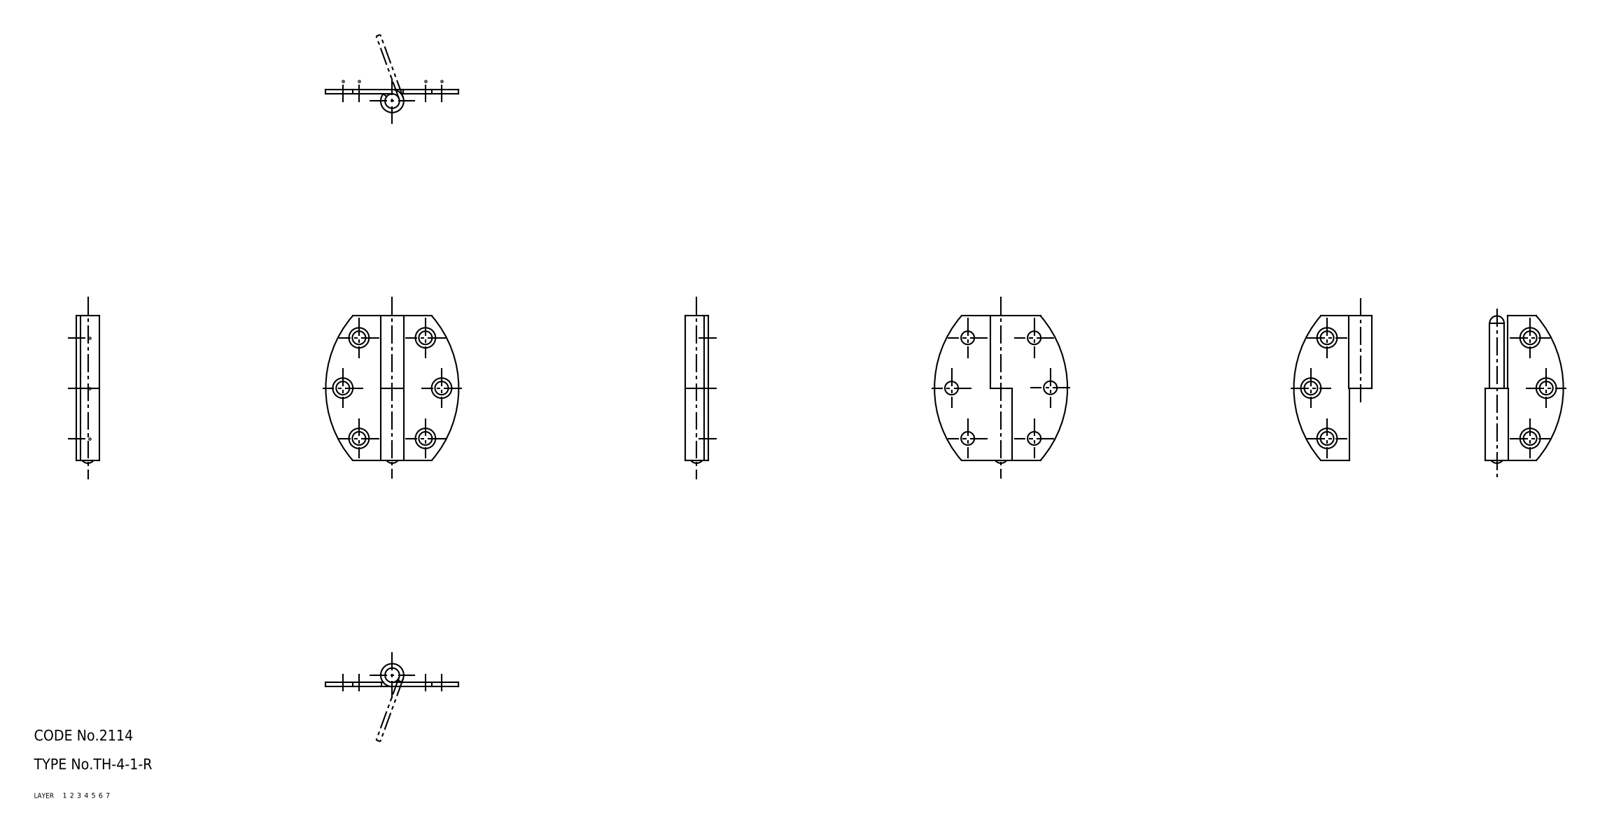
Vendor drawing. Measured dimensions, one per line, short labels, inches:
name: shaft; hinge piece_B; hinge piece_A; TH_4_1_R_8987_36
written by: CADfix (AUTOMOTIVE_DESIGN)
unit: in
bodies: 3 solids, 48 faces (0 planar, 0 cylindrical, 48 other)
size: 1.614 × 1.457 × 0.252
volume: 0.15 in³; area: 6.547 in²
